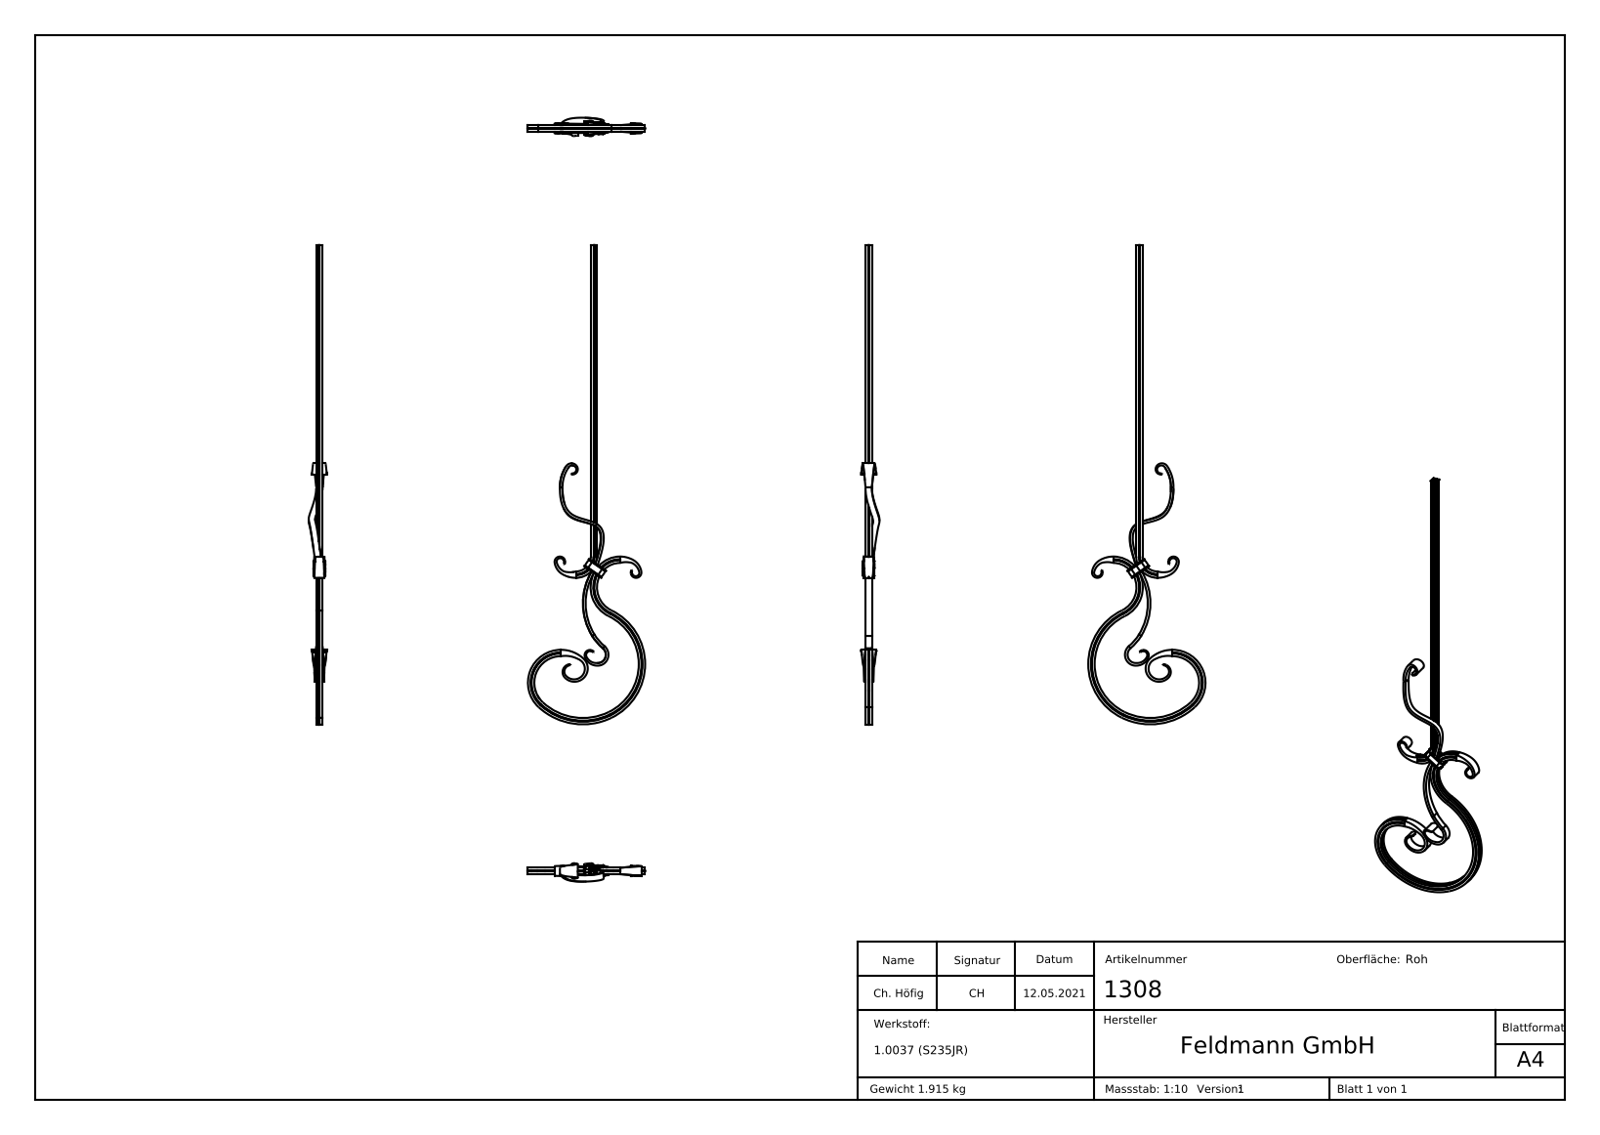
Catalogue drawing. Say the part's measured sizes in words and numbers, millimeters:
The part is named "1308". Its 3-D file was written by "SolidWorks 2018 (CONFIG_CONTROL_DESIGN)". It is 3 solids with 570 faces: 195 planar, 103 cylindrical and 272 other. Overall it measures 900 by 220 by 34.49 millimeters. Its volume is 245 410 cubic millimeters and its surface area 108 967 square millimeters. Partial cylindrical surfaces (rounded edges, fillets, slot ends): 26 of radius 0.2, 8 of radius 0.5, 4 of radius 3, 4 of radius 8, 4 of radius 16.8, 2 of radius 0.25, 1 of radius 28, 1 of radius 40. The main face-to-face distances are 12, 4.6, 4.21, 16, 1, 15, 29.03, 14, 5, 17.
